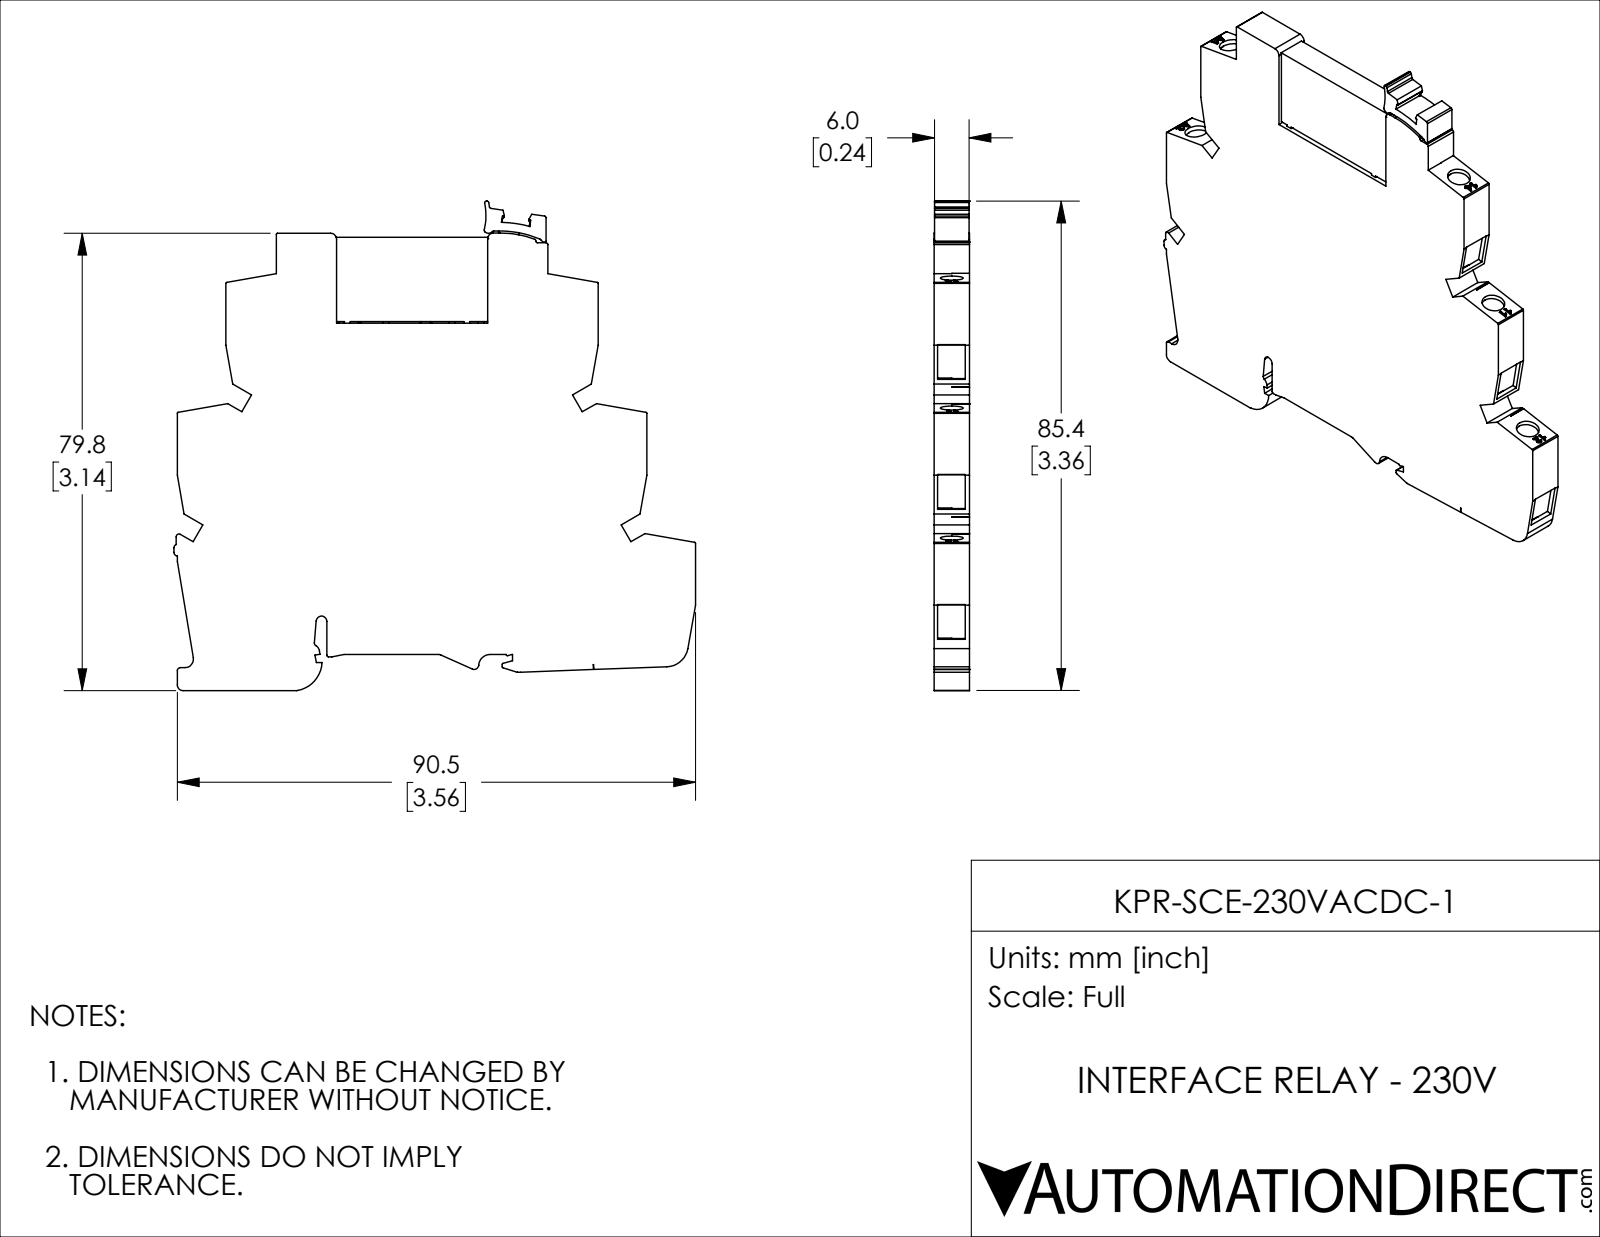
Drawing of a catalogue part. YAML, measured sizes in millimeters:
part_name: "KPR-SCE-230VACDC-1"
step_written_by: "SolidWorks 2018 (AUTOMOTIVE_DESIGN)"
units: millimeters
bodies: {solids: 1, faces: 422, planar: 304, cylindrical: 90, other: 28}
overall_size: [91.1, 85.4, 6.2]
volume: 34480
surface_area: 15190
round_holes:
  - {diameter: 4, count: 5}
round_bosses_or_shafts:
  - {diameter: 0.4, count: 2}
partial_cylinders:
  - {radius: 0.2, count: 15}
  - {radius: 0.3, count: 10}
  - {radius: 1, count: 10}
  - {radius: 0.5, count: 5}
  - {radius: 0.9, count: 5}
  - {radius: 2, count: 3}
  - {radius: 0.1, count: 2}
  - {radius: 0.6, count: 2}
face_to_face_distances: [6.2, 0.6, 5.6, 0.8, 5, 8.5, 0.8, 20.9, 82, 73.5]
hole_center_spacings: [12.3, 12.3, 24.6]
